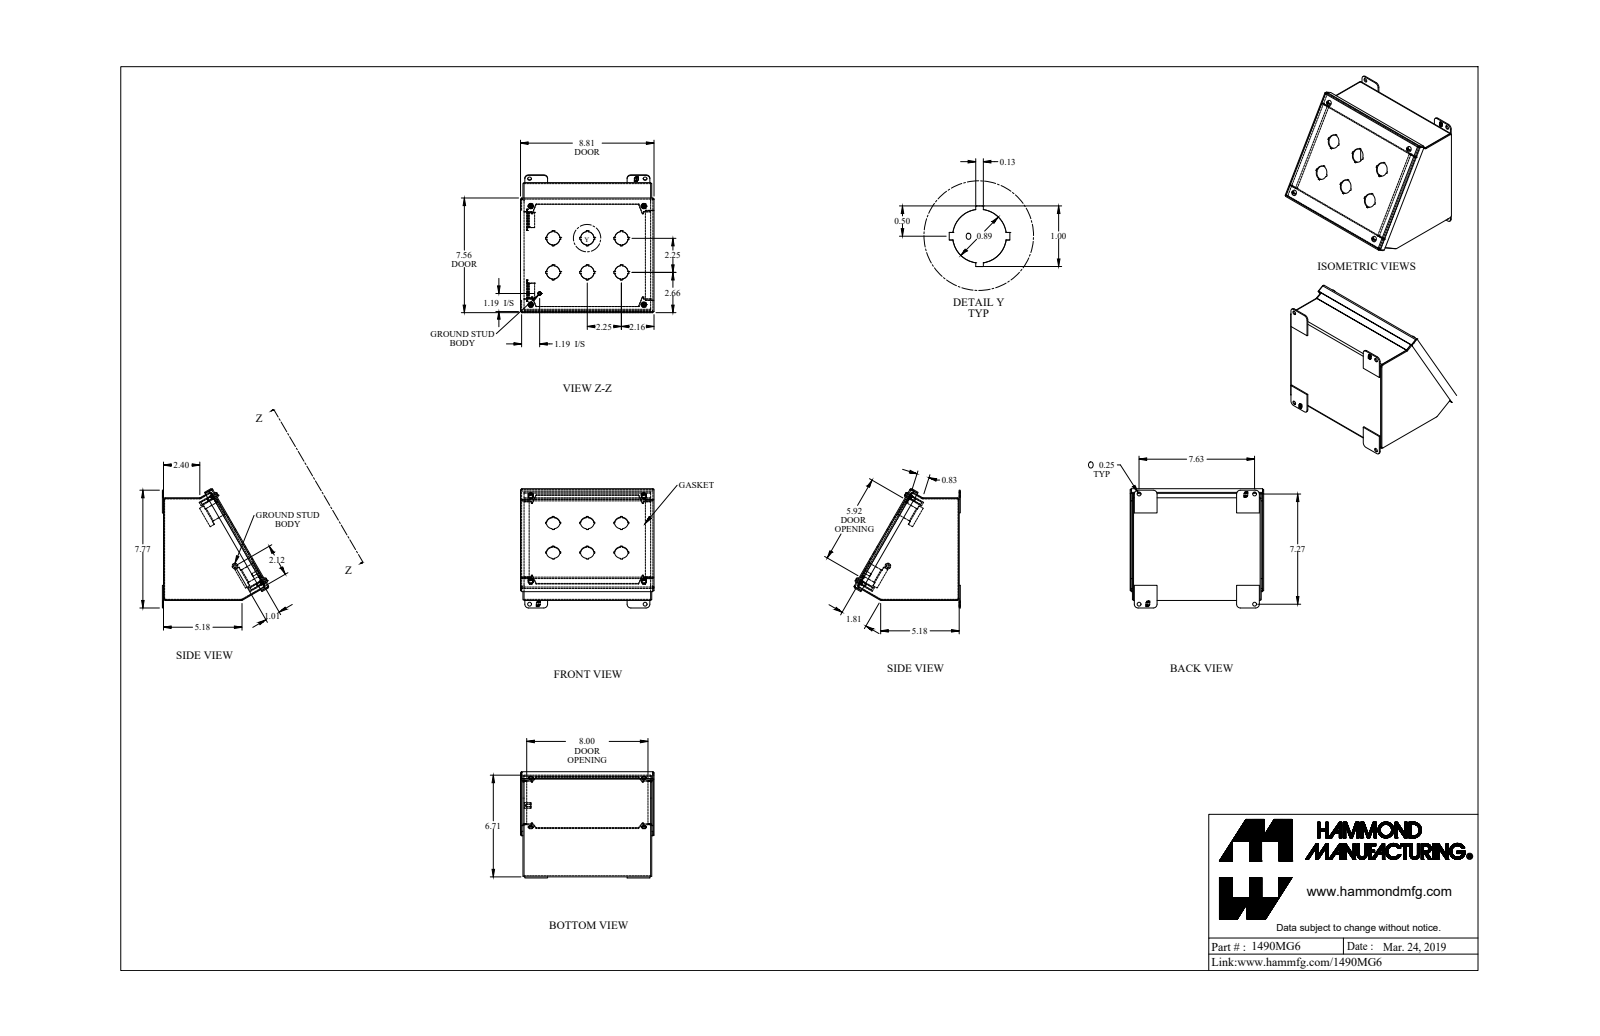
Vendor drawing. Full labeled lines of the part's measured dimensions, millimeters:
Part name (STEP PRODUCT): 1490MG6_Default
STEP written by: SolidWorks 2019 (CONFIG_CONTROL_DESIGN)
Units: millimetres
Bodies: 26 solids, 790 faces (555 planar, 197 cylindrical, 38 other)
Overall size (bounding box): 223.8 × 200.4 × 179.1
Volume: 364 000 mm³ · Surface area: 410 700 mm²
Round holes (diameter × count): ⌀6.4 ×8, ⌀4 ×4, ⌀22.2 ×4, ⌀22.2 ×2, ⌀3 ×1, ⌀3.5 ×1, ⌀4 ×1
Round bosses / shafts (diameter × count): ⌀9.9 ×4, ⌀7 ×4, ⌀4.8 ×4, ⌀3.8 ×4, ⌀9.5 ×1, ⌀7.4 ×1
Partial cylindrical surfaces — rounded edges, fillets, slot ends (radius × count): R2.7 ×18, R0.9 ×12, R0.7 ×9, R2.2 ×9, R6.4 ×8, R3.2 ×4, R4.1 ×4, R4.3 ×4
Main face-to-face distances: 1.8, 214.1, 170.1, 212.2, 215.9, 4, 171.9, 168.3, 186.3, 5.8
Hole centre spacings: 165.1, 57.2, 65.9, 80.8, 109, 109.2, 146.2, 161.4
